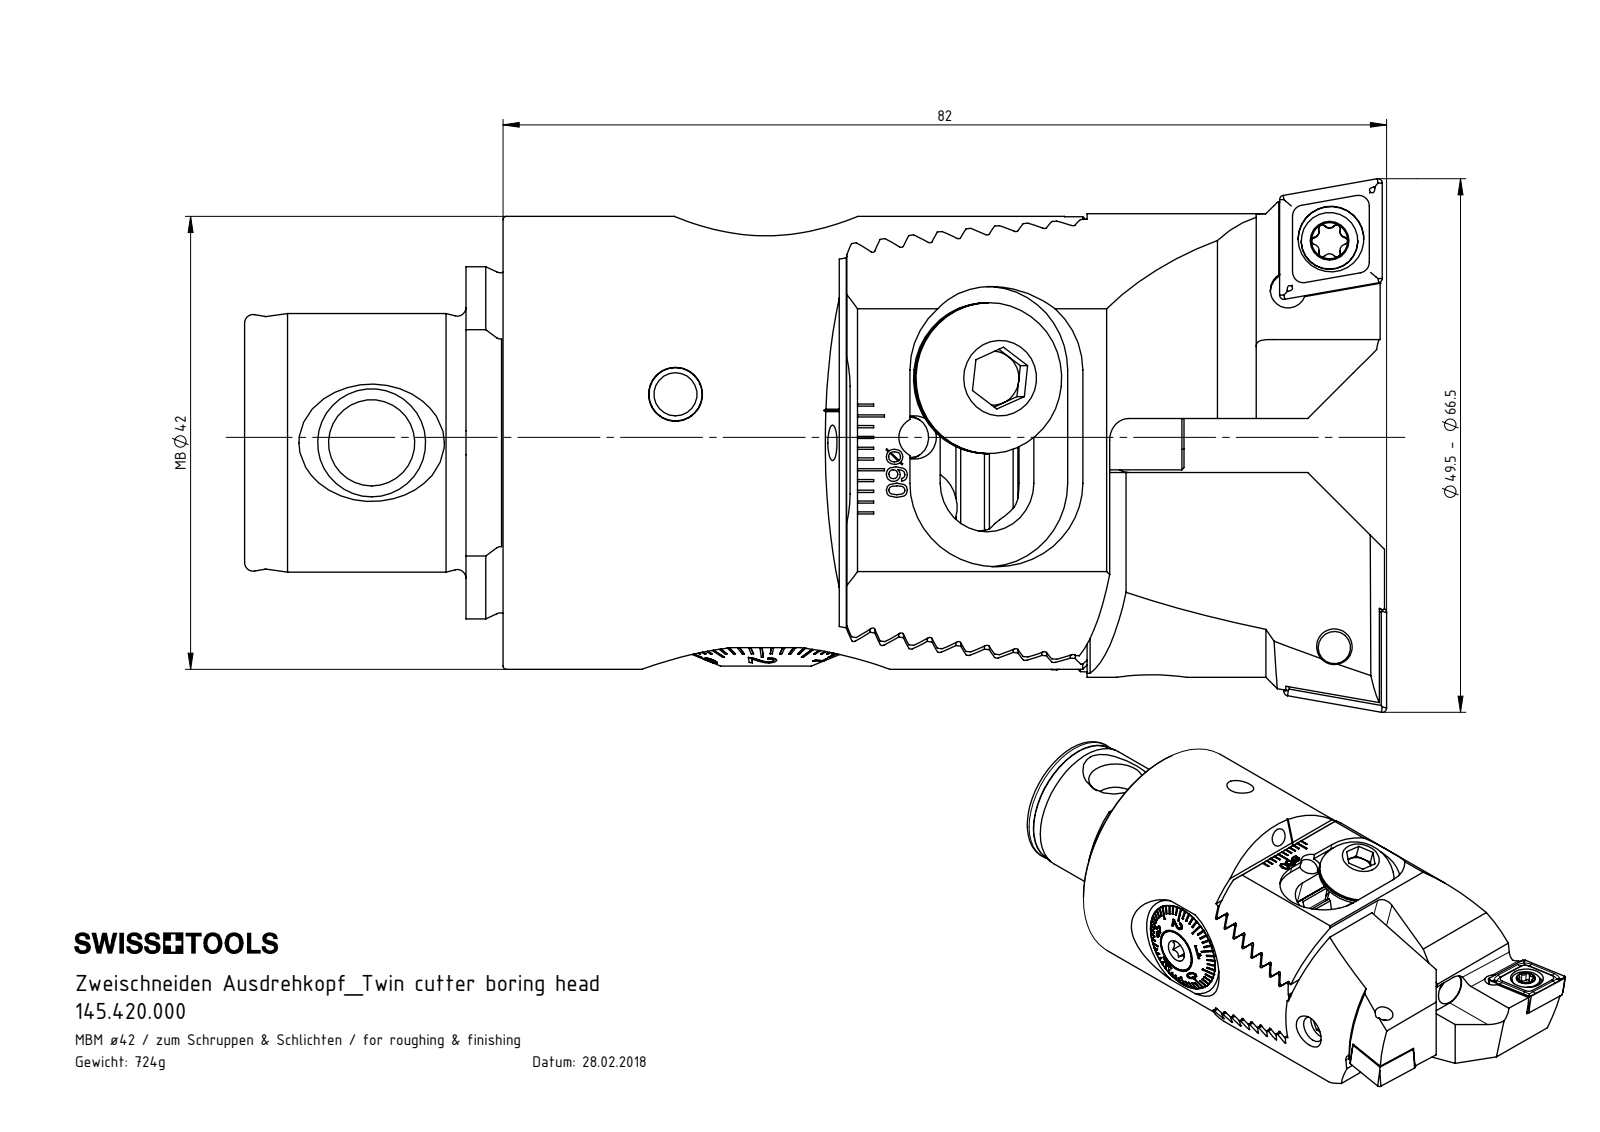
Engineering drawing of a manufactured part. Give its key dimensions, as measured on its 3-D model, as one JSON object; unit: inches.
{"part_name": "MB4-ZC4.K23.082_A; ZC4-xxx.001.028_A_versetzt mit FV; WCB-ER2.001.009_A; CCMT09T304 (+8 more)", "step_written_by": "SolidWorks 2017 (CONFIG_CONTROL_DESIGN)", "units": "inches", "bodies": {"solids": 23, "faces": 1491, "planar": 745, "cylindrical": 283, "other": 463}, "overall_size": [4.173, 1.949, 1.654], "volume_in3": 5.648, "surface_area_in2": 59.11, "round_holes": [[0.13, 8], [0.197, 3], [0.118, 2], [0.173, 2], [0.24, 2], [0.268, 2], [0.331, 2], [0.335, 2], [0.354, 2], [0.063, 1], [0.079, 1], [0.098, 1]], "round_bosses_or_shafts": [[0.157, 5], [0.551, 4], [0.315, 3], [0.207, 2], [1.654, 1], [0.945, 1], [0.669, 1], [0.669, 1]], "partial_cylinders_radius": [[0.008, 18], [0.008, 16], [0.013, 12], [0.023, 12], [0.079, 5], [0.063, 4], [0.177, 4], [0.305, 4]], "face_to_face_distances": [0.094, 0.187, 0.281, 0.092, 0.095, 0.189, 0.375, 0.186, 0.469, 0.469], "hole_center_spacings": [0.244, 1.327, 0.236, 0.239, 0.256, 0.432, 0.472, 0.717]}
